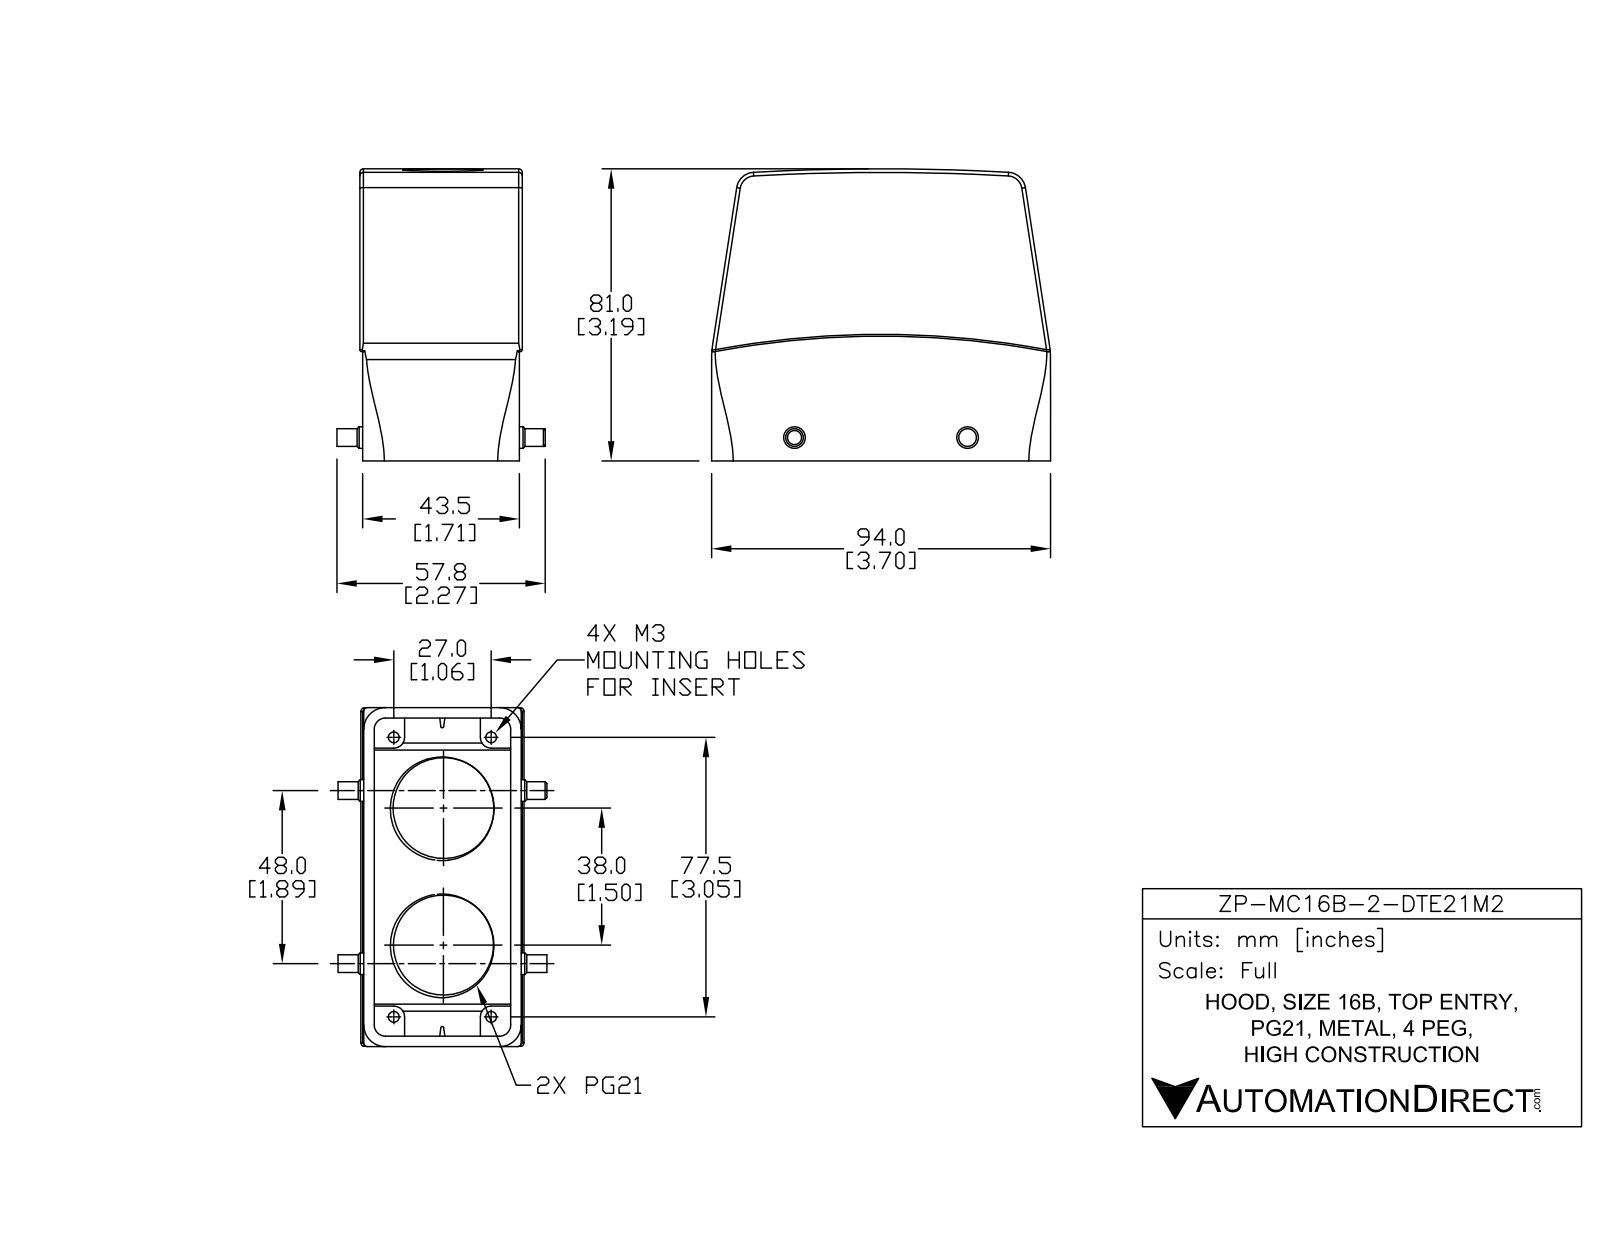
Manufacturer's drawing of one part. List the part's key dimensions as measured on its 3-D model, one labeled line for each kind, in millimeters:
Part name (STEP PRODUCT): ZP-MC16B-2-DTE21M2
STEP written by: SolidWorks 2014 (AUTOMOTIVE_DESIGN)
Units: millimetres
Bodies: 1 solid, 211 faces (57 planar, 118 cylindrical, 36 other)
Overall size (bounding box): 94 × 81 × 57.95
Volume: 82 633 mm³ · Surface area: 46 905 mm²
Round holes (diameter × count): ⌀3 ×4, ⌀27 ×2
Round bosses / shafts (diameter × count): ⌀6 ×2, ⌀4.9 ×2
Partial cylindrical surfaces — rounded edges, fillets, slot ends (radius × count): R1 ×4, R3 ×4, R0.41 ×2, R0.5 ×2, R2.1 ×2, R5 ×2, R30 ×2, R14.74 ×1
Main face-to-face distances: 3.69, 41.55, 37.86, 0.8, 44.44, 2.89, 40.75, 45.24, 2.9, 43.64
Hole centre spacings: 23.92, 59.31, 27, 77.5, 82.07, 38
